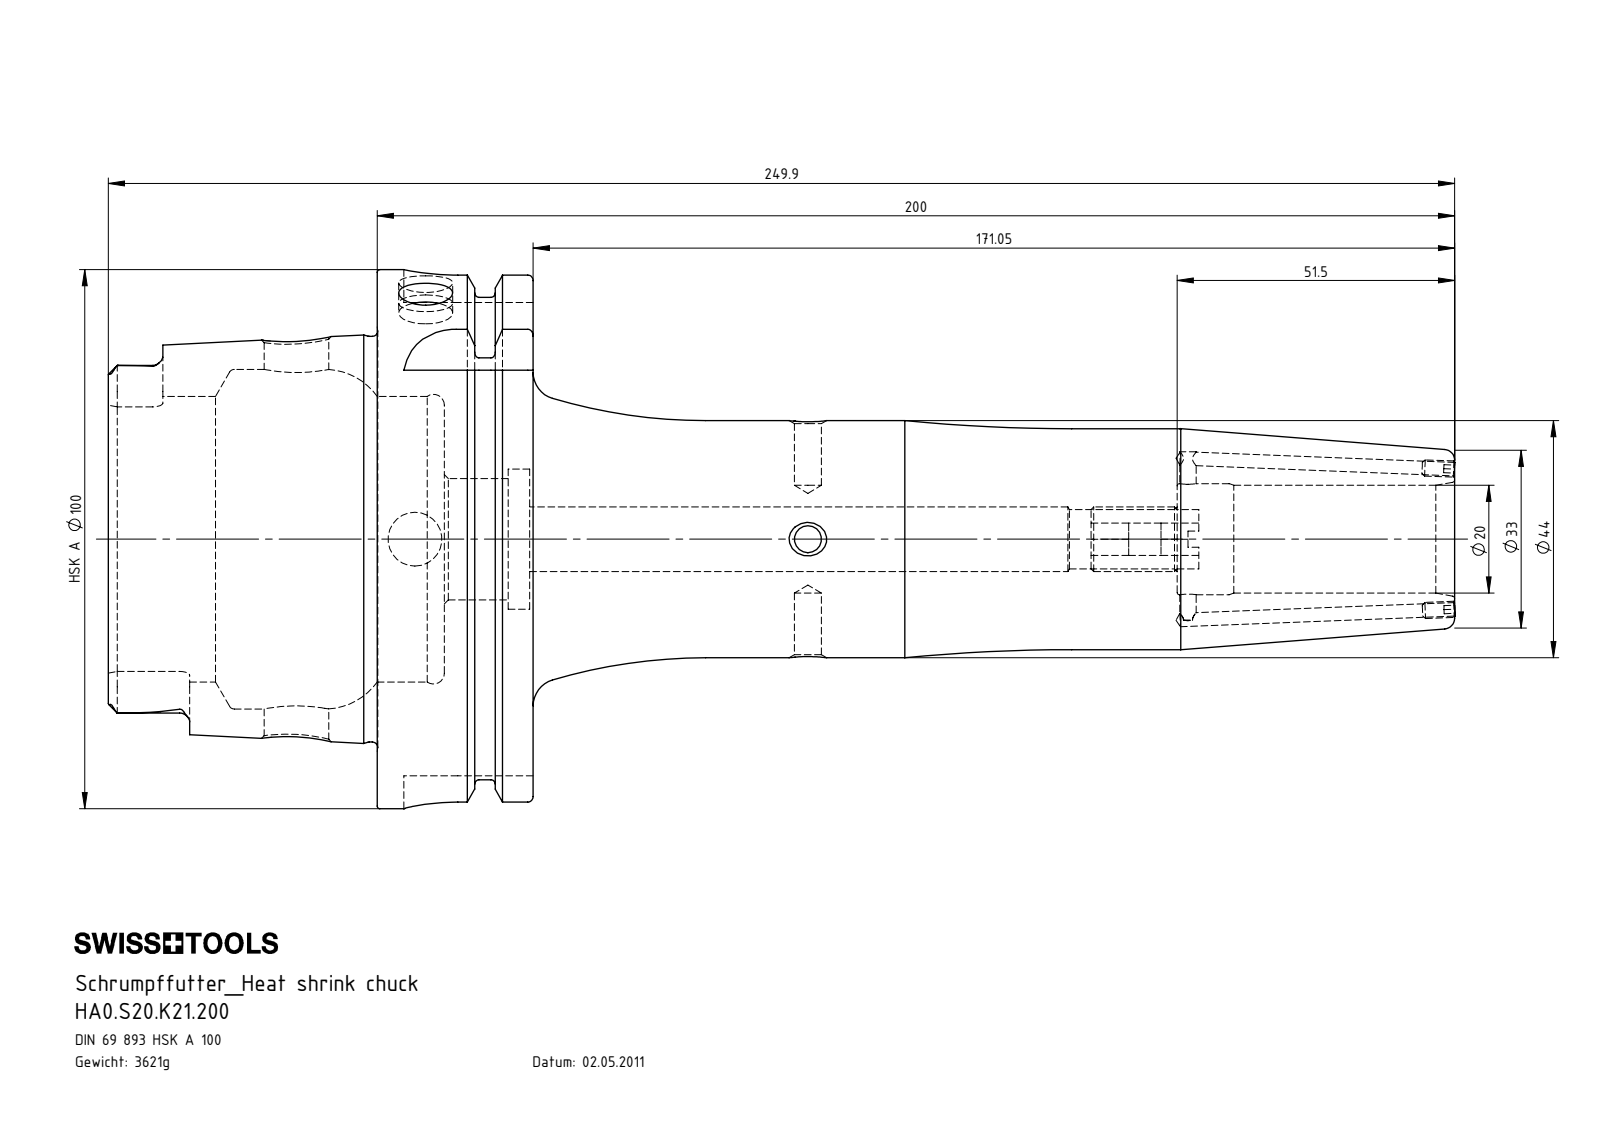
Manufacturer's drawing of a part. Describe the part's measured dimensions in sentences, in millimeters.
The part is named "HA0-S20.K21.200_C_Fertigbearbeitung; ERU-CJ2.001.006; ERU-AN5.K01.020_A; HA0.S20.K21.200". Its 3-D file was written by "SolidWorks 2017 (CONFIG_CONTROL_DESIGN)". It is 4 solids with 305 faces: 95 planar, 87 cylindrical and 123 other. Overall it measures 249.98 by 100 by 100 millimeters. Its volume is 461 288 cubic millimeters and its surface area 81 270 square millimeters. Round holes: 3 of diameter 10, 2 of diameter 2.5, 2 of diameter 5, 2 of diameter 12, 1 of diameter 3, 1 of diameter 6, 1 of diameter 11, 1 of diameter 20, 1 of diameter 20.6, 1 of diameter 22.5, 1 of diameter 26, 1 of diameter 53. Round bosses or shafts: 2 of diameter 3, 1 of diameter 100, 1 of diameter 91.95, 1 of diameter 75.26, 1 of diameter 44, 1 of diameter 41. Partial cylindrical surfaces (rounded edges, fillets, slot ends): 6 of radius 1.9, 4 of radius 4.88, 4 of radius 10. The main face-to-face distances are 28.95, 12.45, 16.5, 49.9, 62.35, 78.85, 87.8, 78.2, 28.3, 15.85. The hole center spacings are 70.55, 72.95, 94.95, 165.5.
